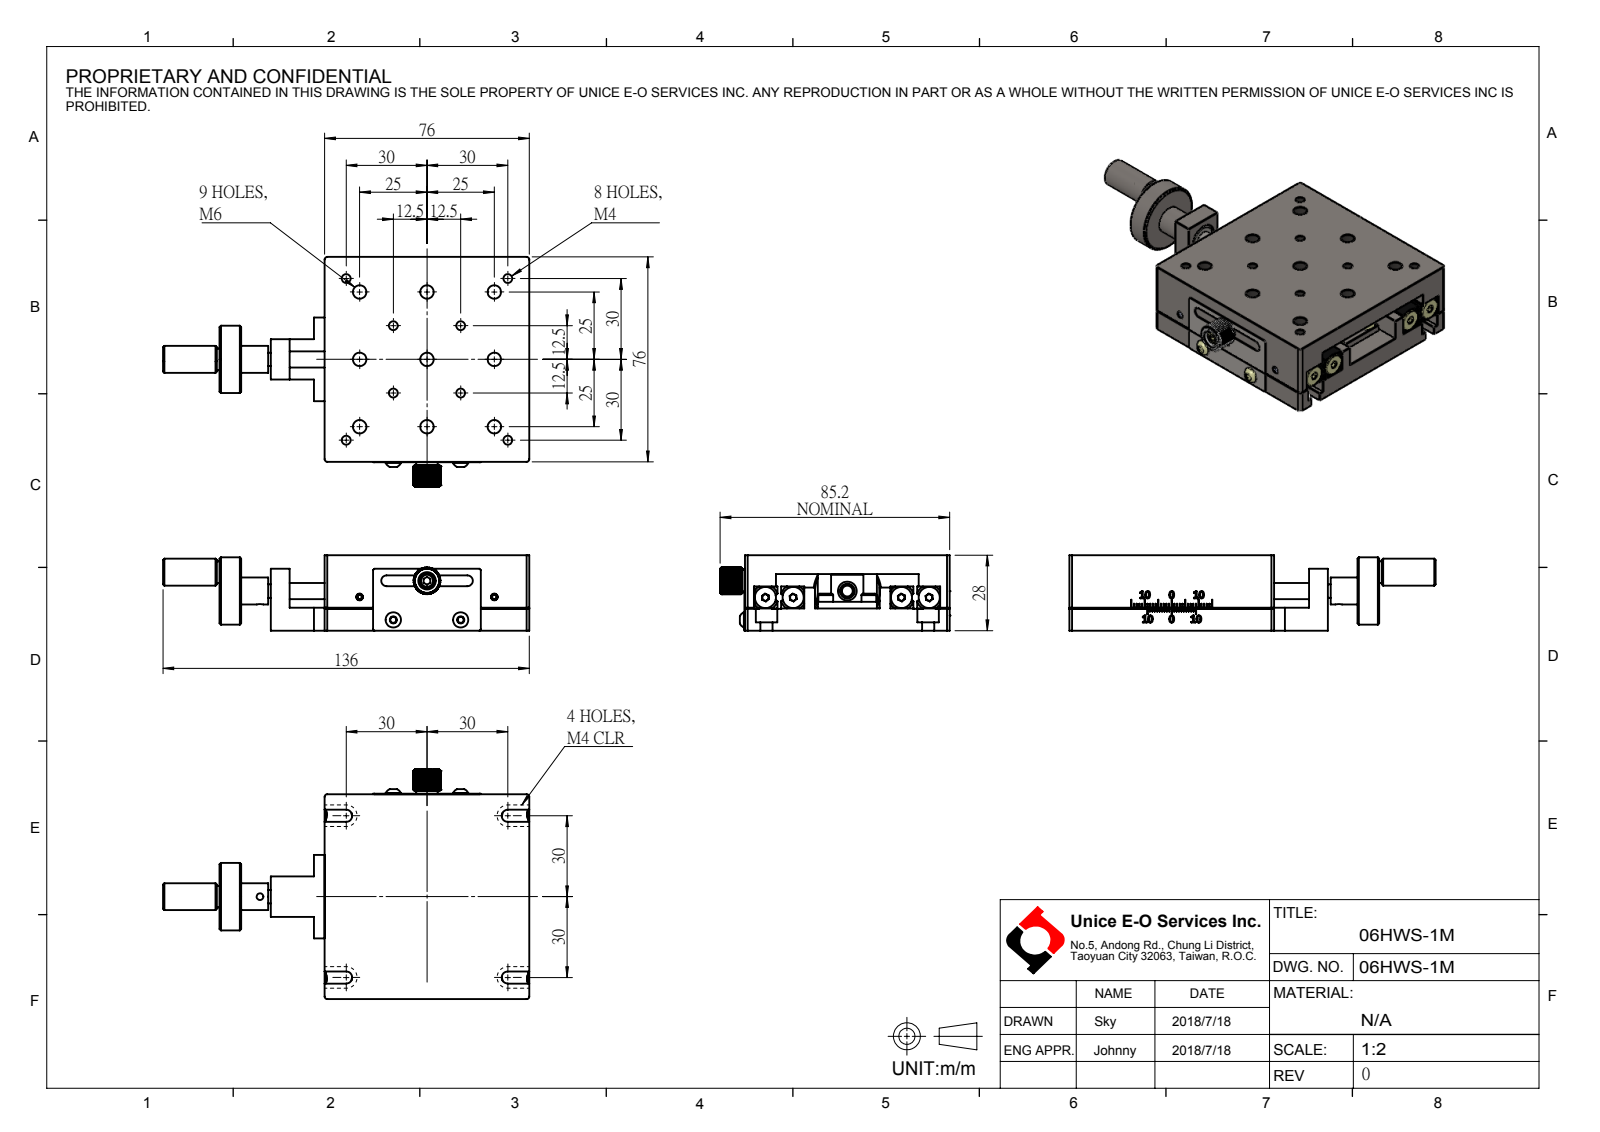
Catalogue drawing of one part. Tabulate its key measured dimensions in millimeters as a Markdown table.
| quantity | value |
| --- | --- |
| part name | 06HWS-1M |
| STEP written by | SolidWorks 2022 (CONFIG_CONTROL_DESIGN) |
| units | millimeters |
| bodies | 58 solids, 1676 faces (1151 planar, 272 cylindrical, 253 other) |
| overall size | 136 × 86 × 28 |
| volume | 138 875 mm³ |
| surface area | 73 260 mm² |
| round holes (diameter × count) | 2.5 × 28, 3.5 × 16, 6 × 15, 3.3 × 12, 5 × 11, 3.4 × 6, 4.5 × 4, 6.5 × 4, 3 × 2, 3.1 × 2, 3.2 × 2, 7 × 2 |
| round bosses / shafts (diameter × count) | 3 × 25, 5.5 × 22, 7.85 × 4, 3.9 × 4, 10 × 2, 8 × 2, 6 × 2, 5.6 × 2 |
| partial cylindrical surfaces (radius × count) | 2 × 8, 1 × 4, 2.25 × 4, 4 × 4, 5 × 1, 10 × 1 |
| main face-to-face distances | 8.2, 28, 19.8, 7, 12.8, 21, 4.6, 11.6, 16.4, 76 |
| hole center spacings | 25, 17.68, 39.53, 35.36, 50, 25.71, 14.33, 25.6 |
